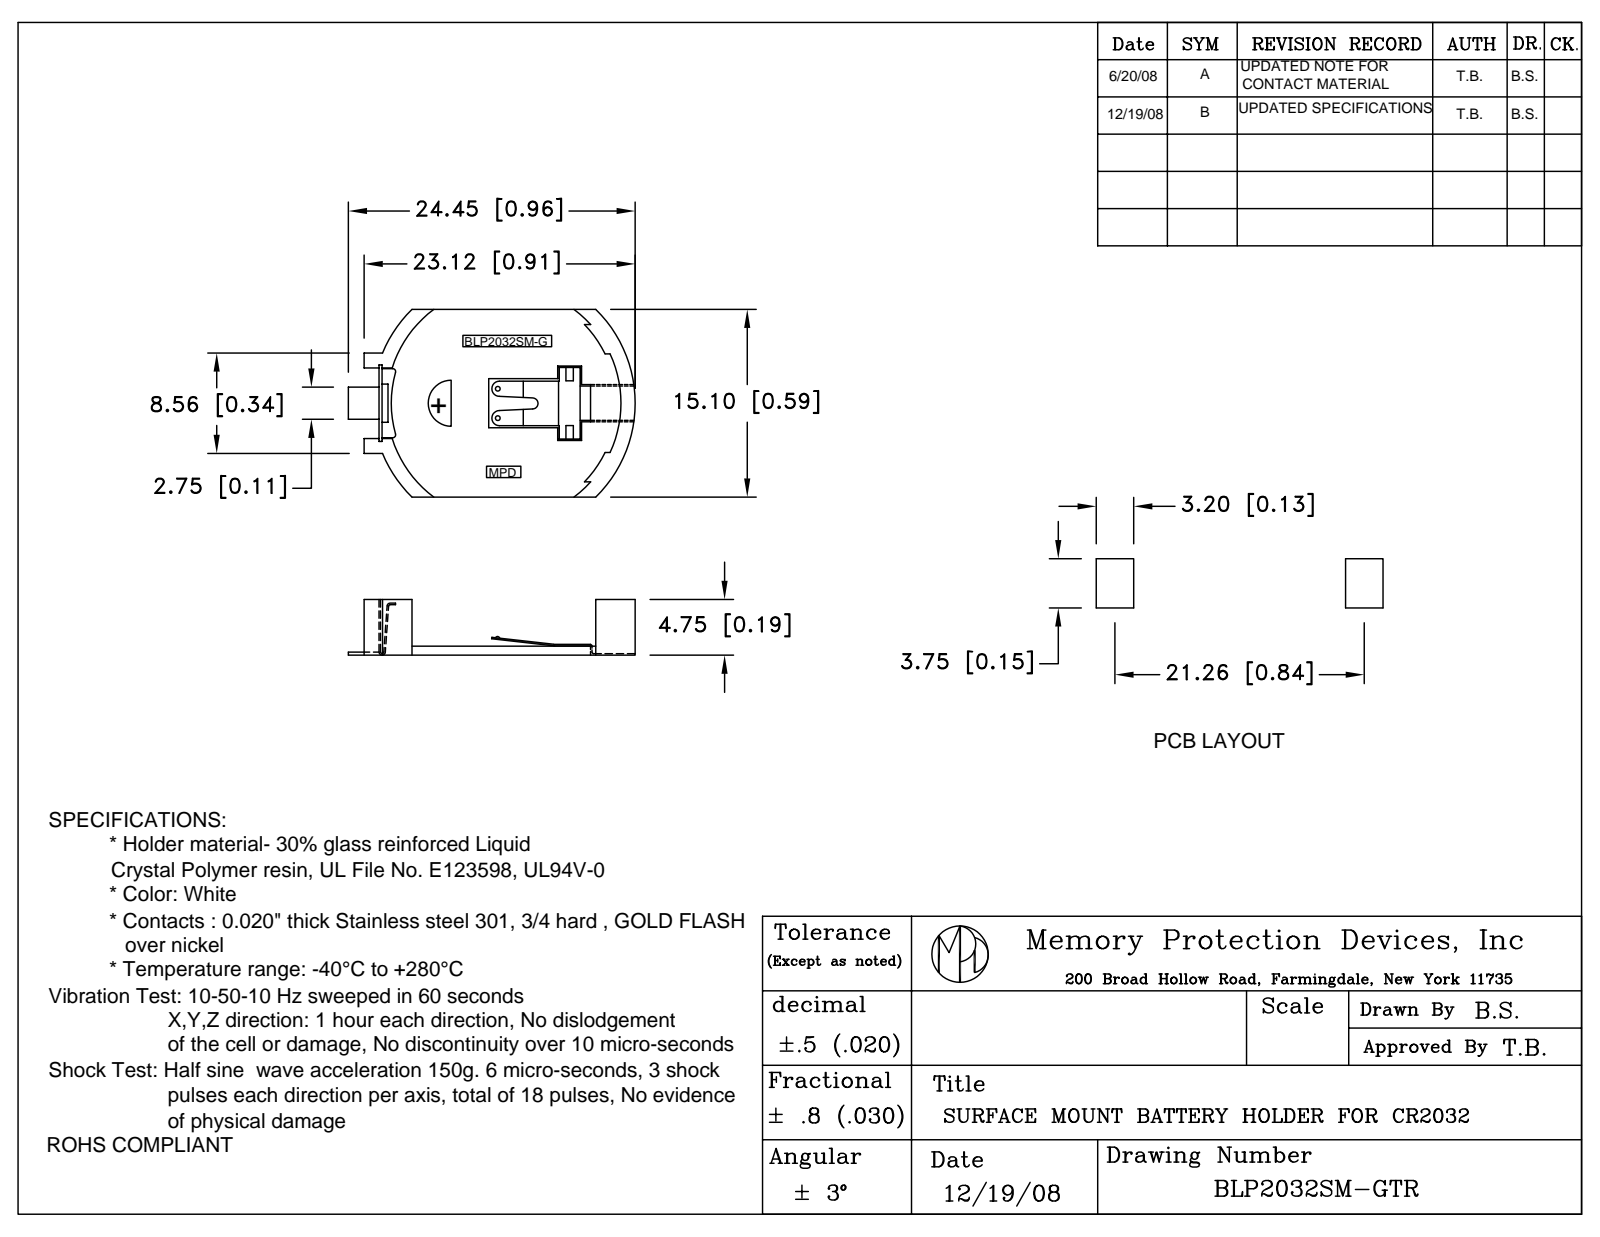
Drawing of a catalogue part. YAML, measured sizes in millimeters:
part_name: "BLP2032SM-GTR"
step_written_by: "SolidWorks 2017 (AUTOMOTIVE_DESIGN)"
units: millimeters
bodies: {solids: 3, faces: 190, planar: 151, cylindrical: 32, other: 7}
overall_size: [24.45, 15.1, 4.75]
volume: 406
surface_area: 1173
partial_cylinders:
  - {radius: 0.2, count: 2}
  - {radius: 0.53, count: 2}
  - {radius: 0.1, count: 1}
  - {radius: 0.15, count: 1}
  - {radius: 0.3, count: 1}
  - {radius: 0.35, count: 1}
  - {radius: 0.41, count: 1}
  - {radius: 0.46, count: 1}
face_to_face_distances: [0.75, 4, 4.75, 0.31, 0.45, 4.45, 15.1, 4.3, 4.65, 1.71]
